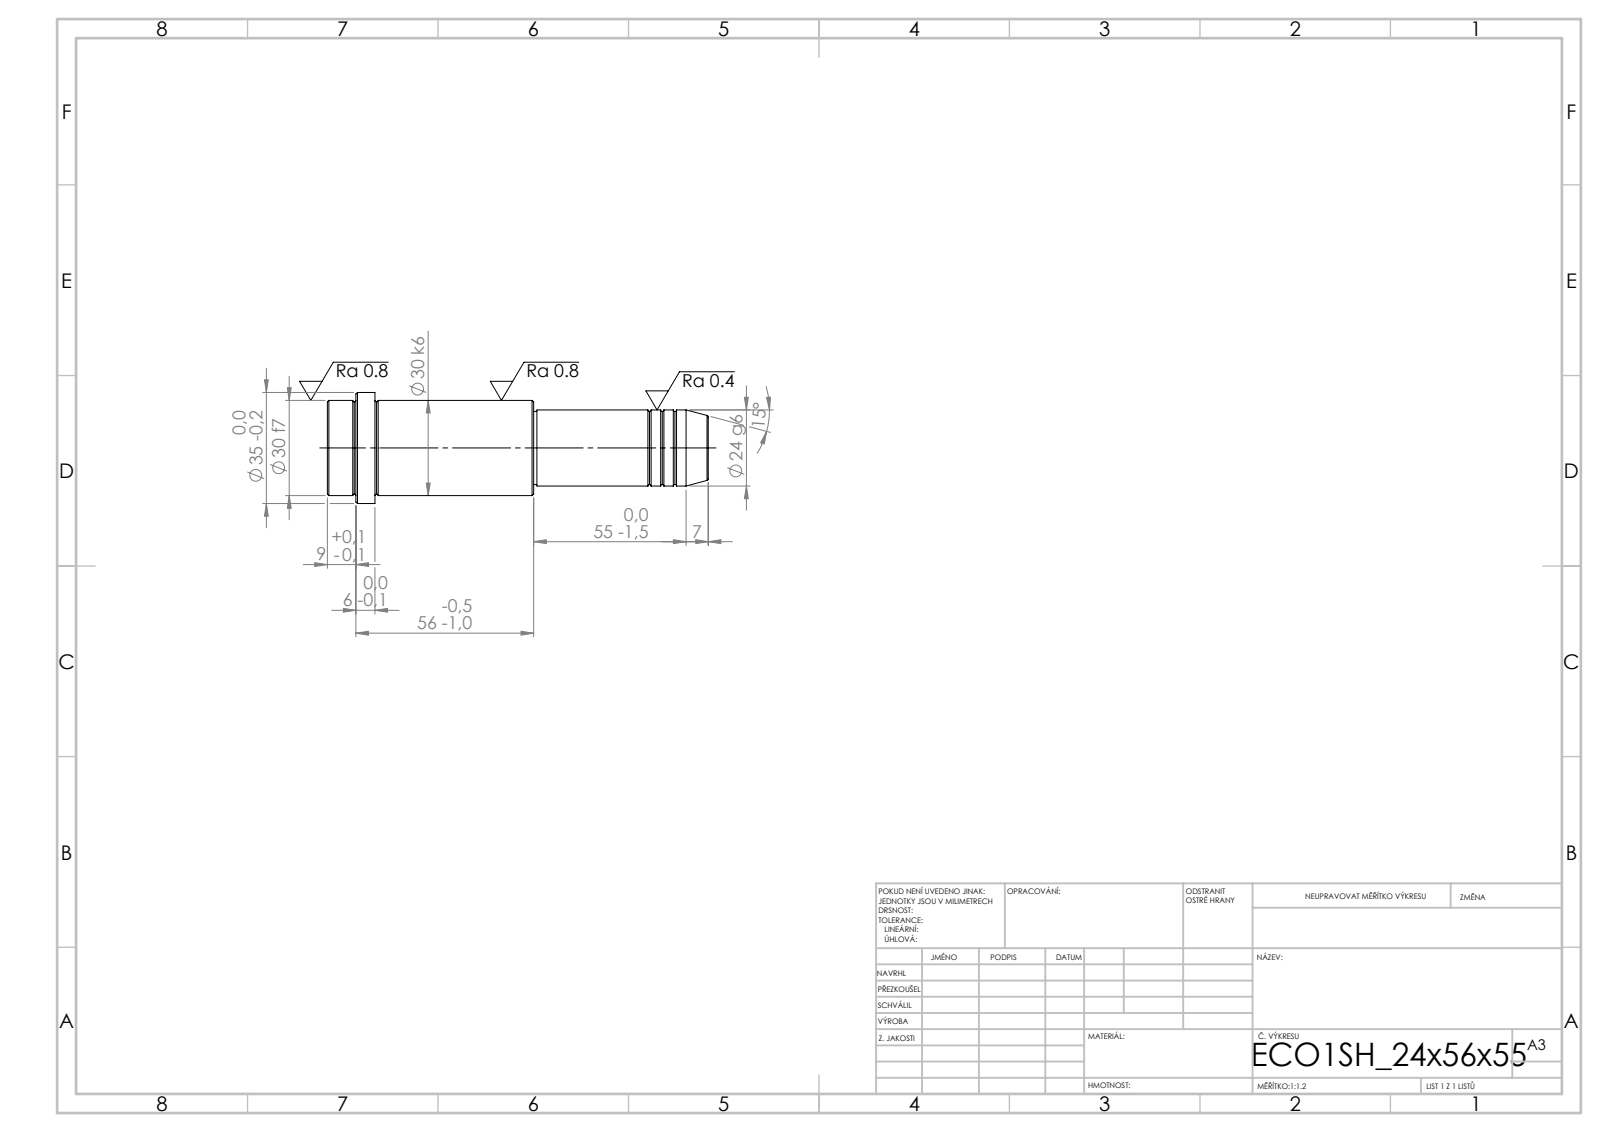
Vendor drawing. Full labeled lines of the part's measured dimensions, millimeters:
STEP written by: SolidWorks 2019 (CONFIG_CONTROL_DESIGN)
Units: millimetres
Bodies: 1 solid, 52 faces (6 planar, 16 cylindrical, 30 other)
Overall size (bounding box): 120 × 35 × 35
Volume: 71 654 mm³ · Surface area: 12 333 mm²
Round bosses / shafts (diameter × count): ⌀35 ×1, ⌀30 ×1, ⌀24 ×1, ⌀23 ×1
Main face-to-face distances: 120, 105, 15, 55, 50, 65, 111, 56, 6, 9
